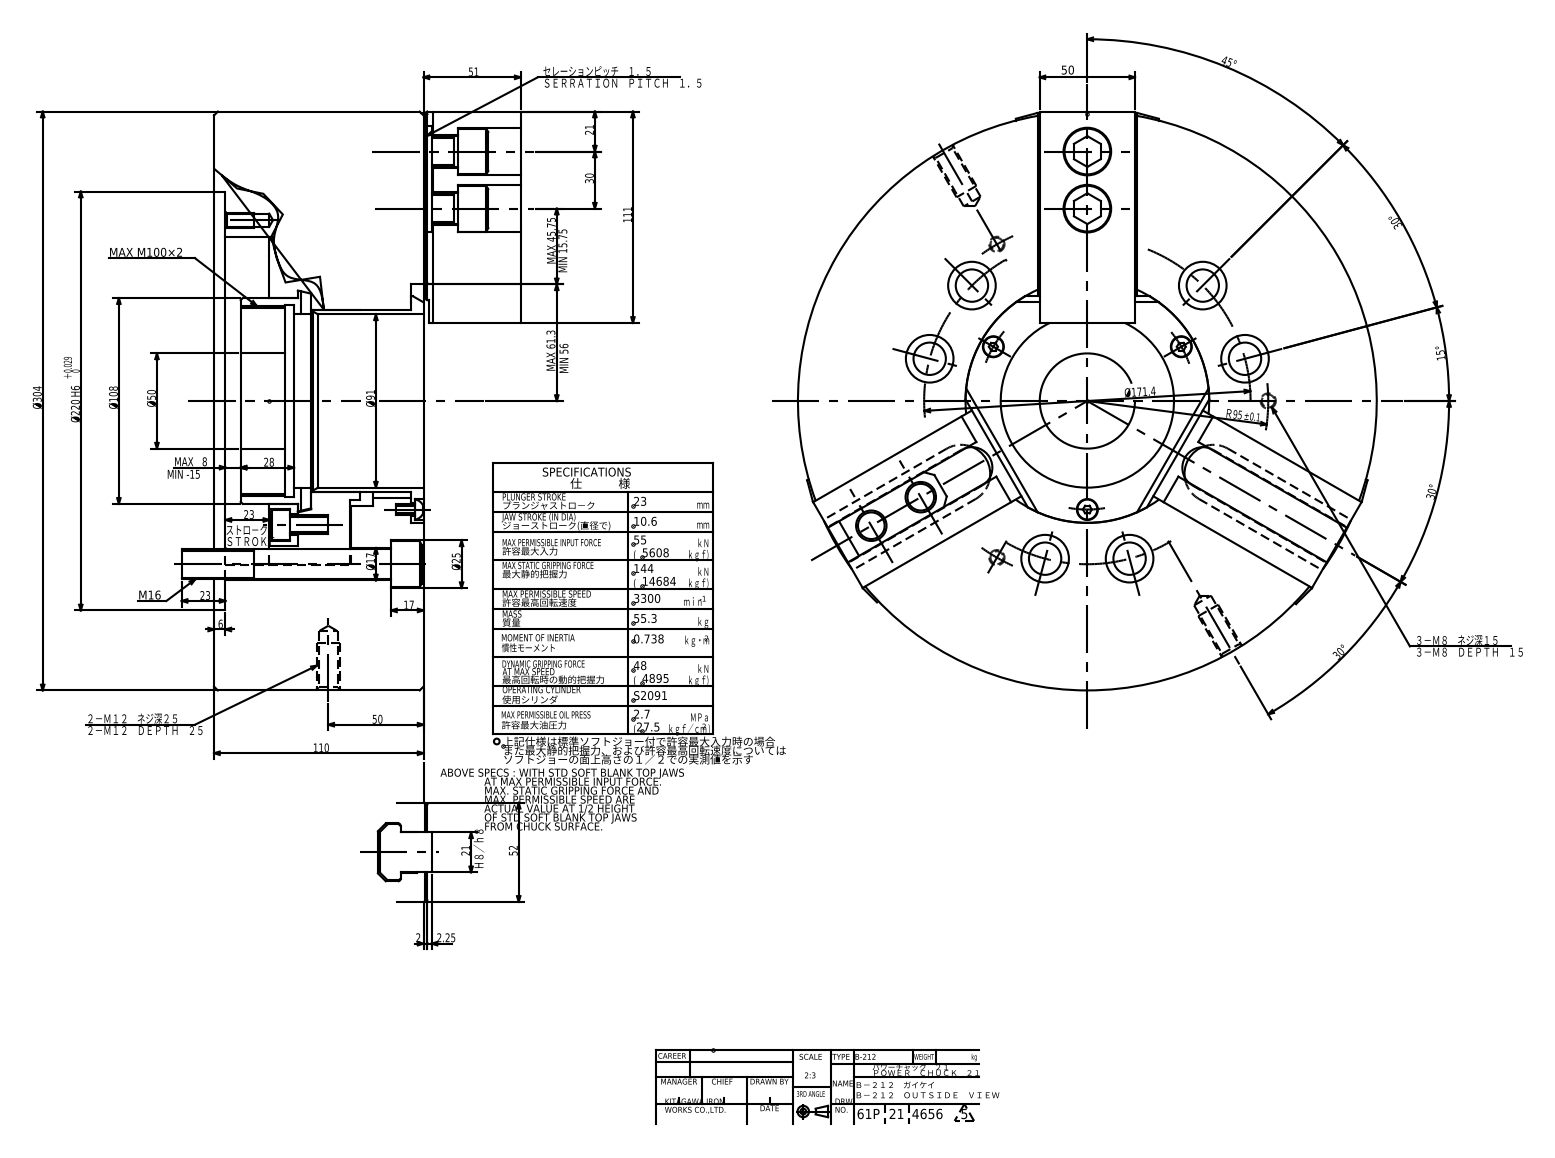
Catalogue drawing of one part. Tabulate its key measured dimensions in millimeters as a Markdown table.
| quantity | value |
| --- | --- |
| part name | B212 solid part |
| STEP written by | ST-DEVELOPER v16.7 (AUTOMOTIVE_DESIGN) |
| units | millimeters |
| bodies | 1 solid, 3602 faces (3152 planar, 206 cylindrical, 244 other) |
| overall size | 304 × 304 × 178.2 |
| volume | 7 572 000 mm³ |
| surface area | 509 256 mm² |
| round holes (diameter × count) | 14 × 12, 17 × 12, 25 × 12, 3.8 × 6, 16 × 6, 1.9 × 3, 6 × 3, 6.6 × 3, 6.92 × 3, 8 × 3, 11 × 3, 15 × 3 |
| round bosses / shafts (diameter × count) | 24 × 12, 16 × 6, 10.5 × 3, 6 × 3, 304 × 1, 108 × 1 |
| partial cylindrical surfaces (radius × count) | 0.6 × 12, 0.45 × 6, 0.8 × 6, 1.4 × 6, 2.59 × 3, 10.8 × 3, 15.25 × 3, 57.77 × 1 |
| main face-to-face distances | 110, 50, 6.46, 103.54, 24.5, 18.04, 85.5, 161.2, 154.74, 136.7 |
| hole center spacings | 31.01, 43.66, 114.57, 148.48, 34.03, 85.72, 96.04, 105.75 |
